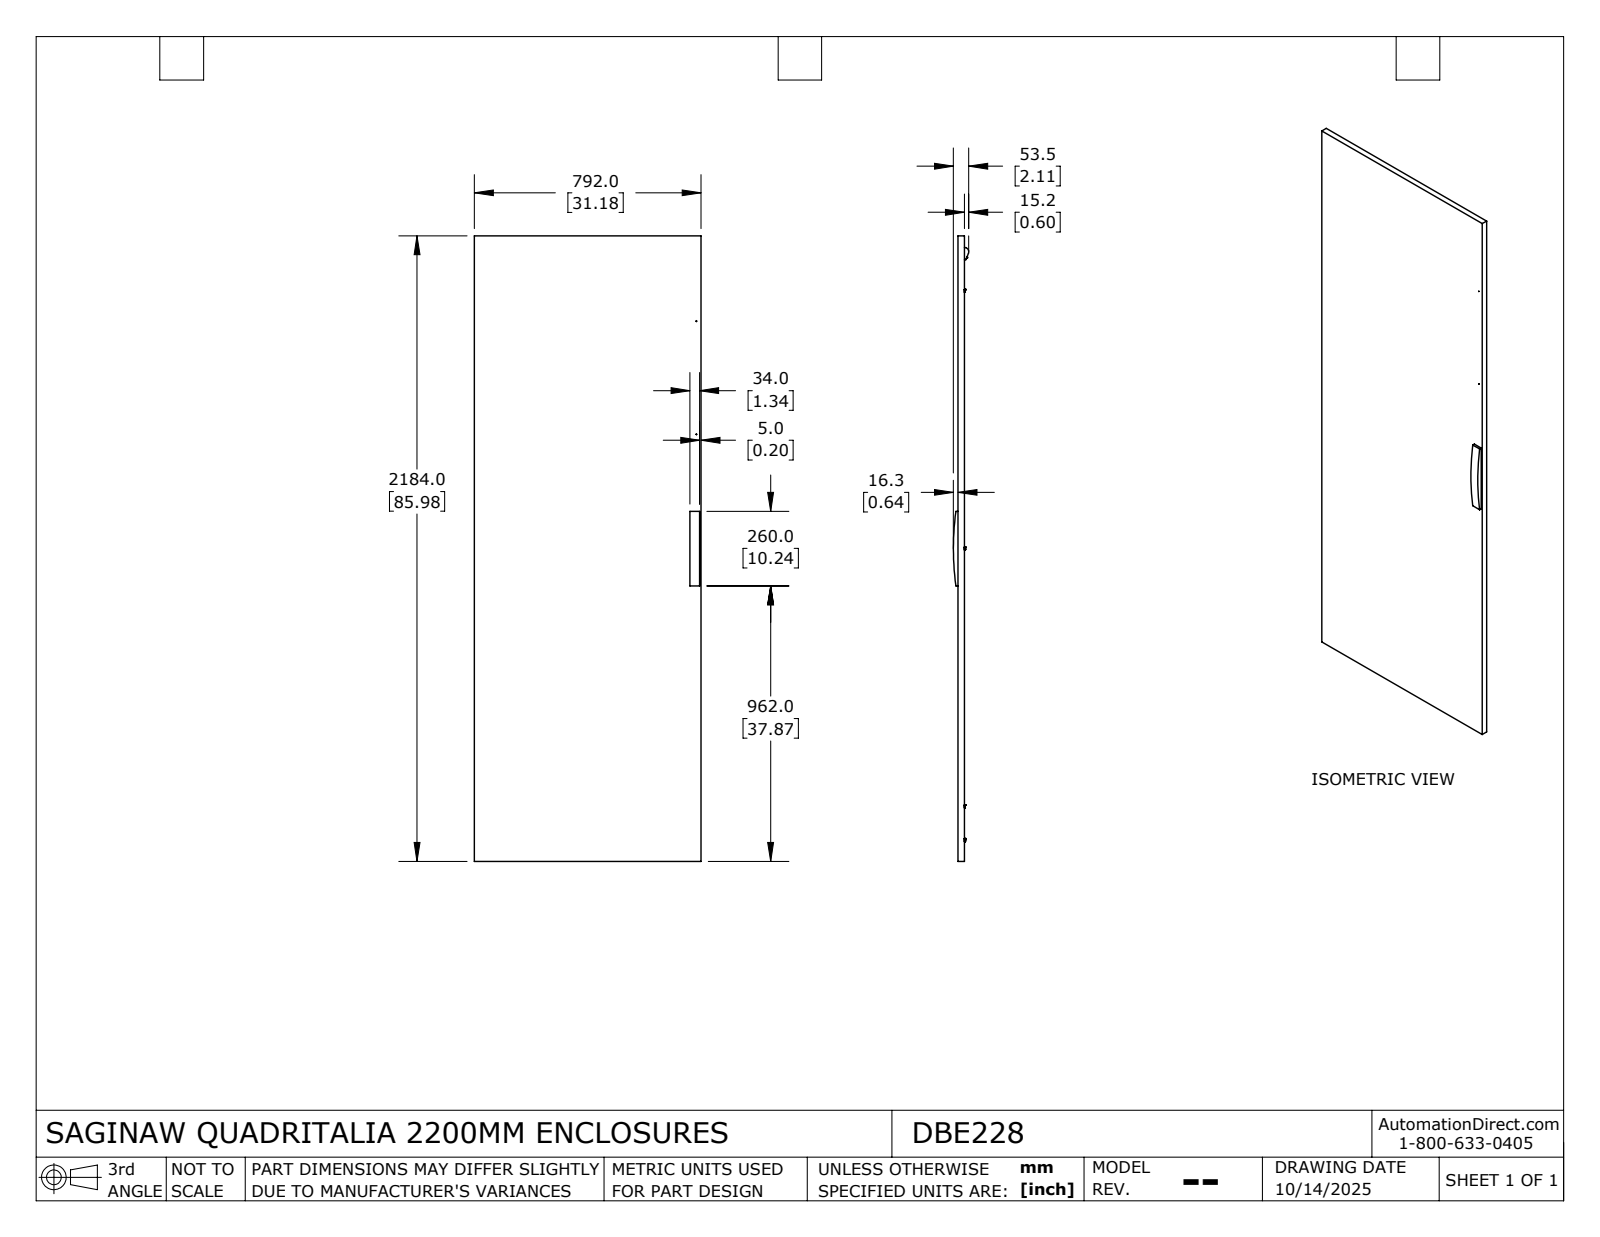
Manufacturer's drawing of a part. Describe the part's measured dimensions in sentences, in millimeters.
The part is named "DBE228; DBE228_Default". Its 3-D file was written by "SolidWorks 2024 (CONFIG_CONTROL_DESIGN)". It is 1 solid with 738 faces: 364 planar, 250 cylindrical and 124 other. Overall it measures 2184 by 792 by 53.5 millimeters. Its volume is 6 382 000 cubic millimeters and its surface area 4 025 000 square millimeters. Round holes: 168 of diameter 4.25, 12 of diameter 9, 10 of diameter 4.92, 2 of diameter 1, 2 of diameter 4.5. Round bosses or shafts: 2 of diameter 7, 2 of diameter 6. Partial cylindrical surfaces (rounded edges, fillets, slot ends): 10 of radius 5.77, 4 of radius 7.52, 2 of radius 6, 1 of radius 15.09, 1 of radius 962.86. The main face-to-face distances are 2, 20, 22, 790, 56, 736, 54, 734, 76, 716. The hole center spacings are 25, 50, 75, 100, 125, 150, 175, 200.
